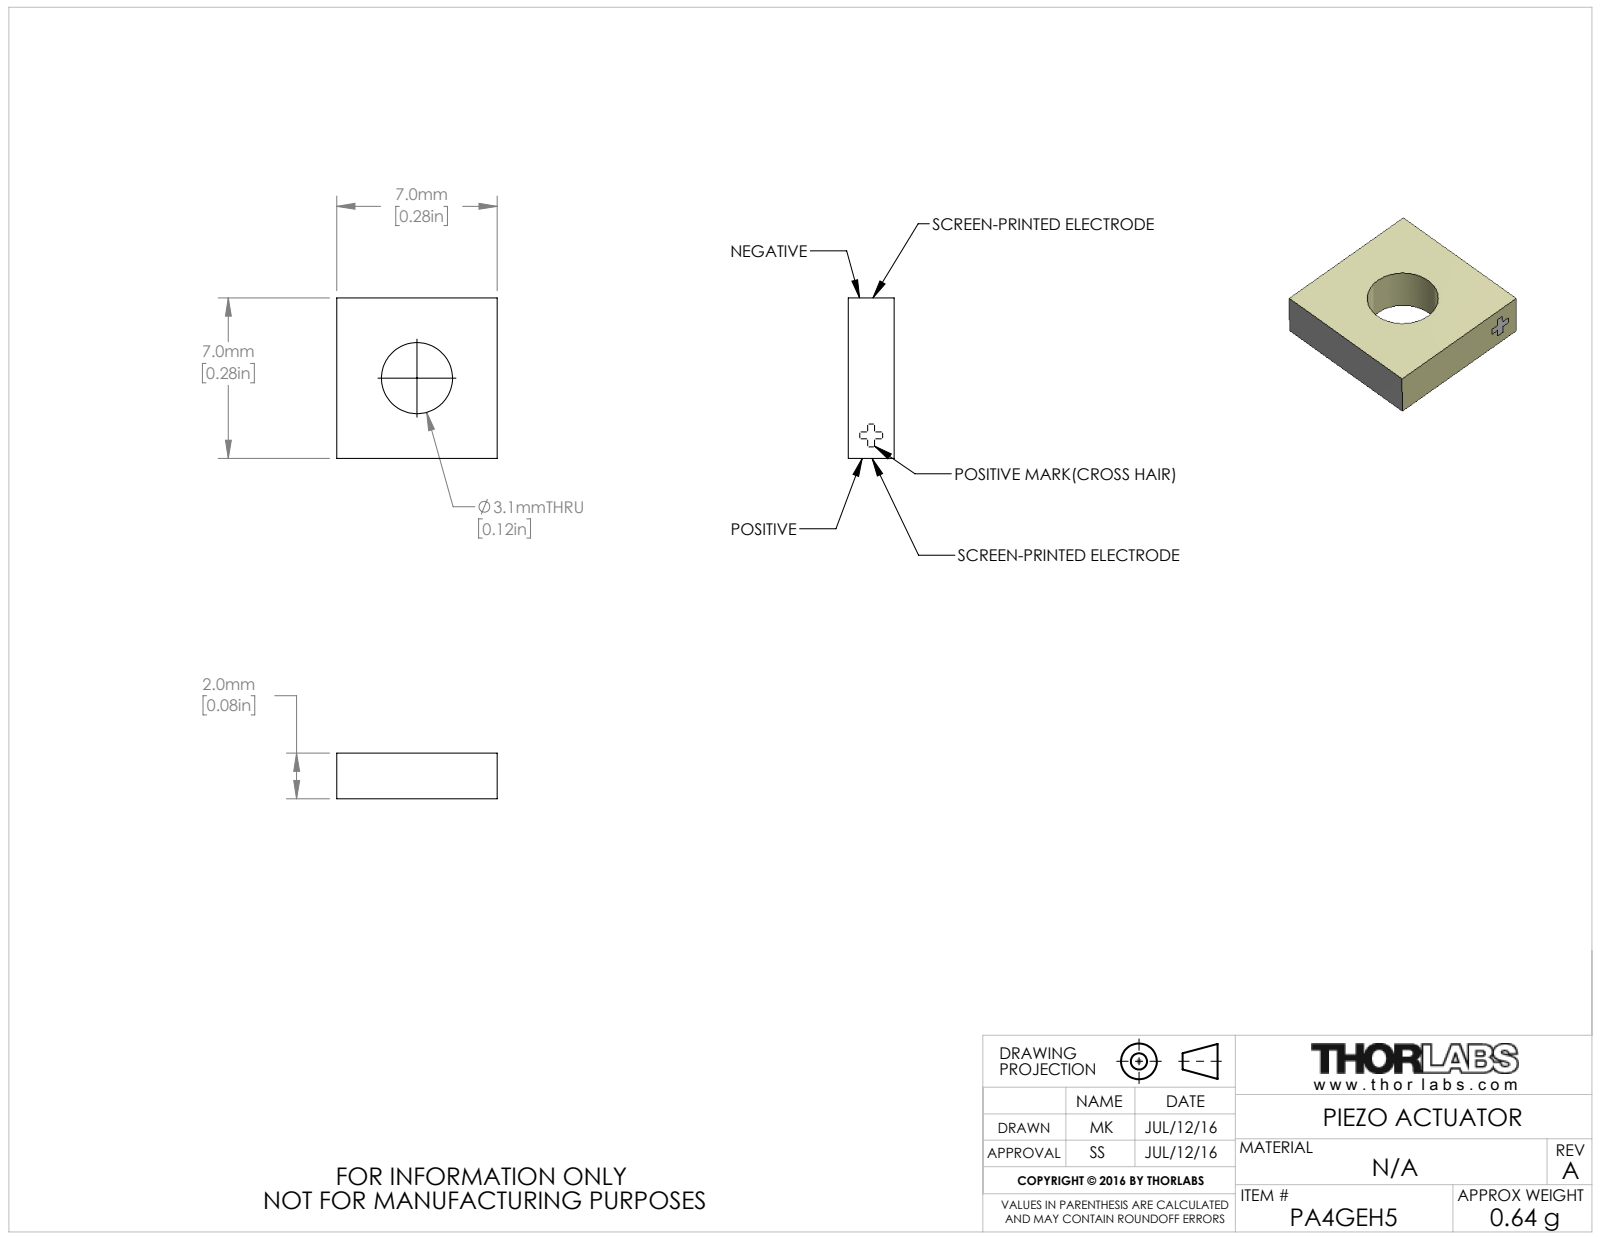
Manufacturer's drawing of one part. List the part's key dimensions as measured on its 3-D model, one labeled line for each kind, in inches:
Part name (STEP PRODUCT): CTN009263
STEP written by: SolidWorks 2016 (AUTOMOTIVE_DESIGN)
Units: inches
Bodies: 1 solid, 9 faces (7 planar, 2 cylindrical, 0 other)
Overall size (bounding box): 0.276 × 0.276 × 0.079
Volume: 0.005 in³ · Surface area: 0.245 in²
Round holes (diameter × count): ⌀0.122 ×1
Main face-to-face distances: 0.079, 0.276
